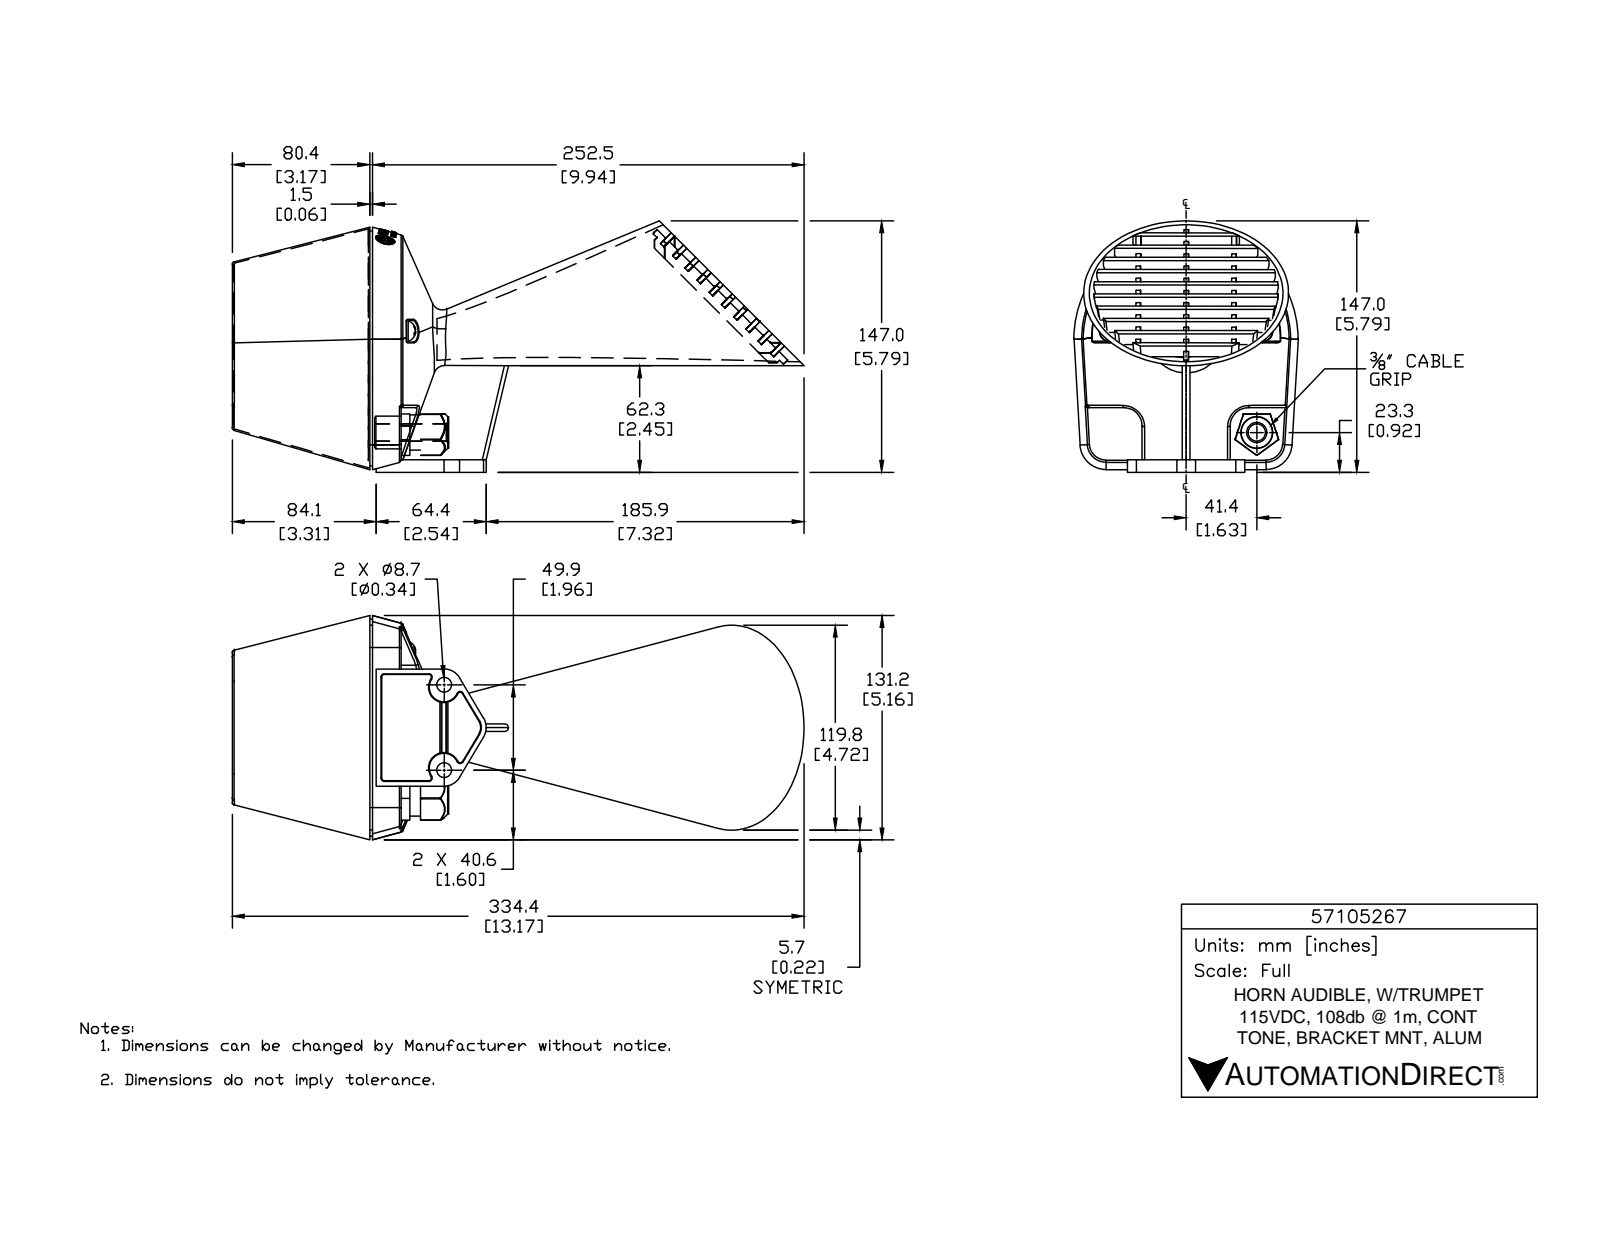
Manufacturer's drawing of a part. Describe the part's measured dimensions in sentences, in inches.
The part is named "57105267_MAIN; 57105267_WASHER; 571_3D Modell; round head screw_ai_CR-RHMS 0.25-28x0.25x0.25-N (+3 more)". Its 3-D file was written by "SolidWorks 2014 (AUTOMOTIVE_DESIGN)". It is 8 solids with 449 faces: 218 planar, 97 cylindrical and 134 other. Overall it measures 13.167 by 5.789 by 5.165 inches. Its volume is 38.84 cubic inches and its surface area 378.1 square inches. Round holes: 2 of diameter 0.188, 2 of diameter 0.313, 2 of diameter 0.343, 1 of diameter 0.4, 1 of diameter 0.463, 1 of diameter 0.5. Round bosses or shafts: 2 of diameter 0.25, 1 of diameter 0.813, 1 of diameter 0.75, 1 of diameter 0.719, 1 of diameter 0.5. Partial cylindrical surfaces (rounded edges, fillets, slot ends): 12 of radius 0.015, 6 of radius 0.06, 5 of radius 0.42, 3 of radius 0.05, 2 of radius 0.02, 2 of radius 0.03, 2 of radius 0.09, 2 of radius 0.355. The main face-to-face distances are 0.795, 0.107, 0.03, 3.226, 3.196, 0.398, 1.59, 0.397, 1.193, 0.687. The hole center spacings are 1.965, 2.336, 3.5, 4.106.
